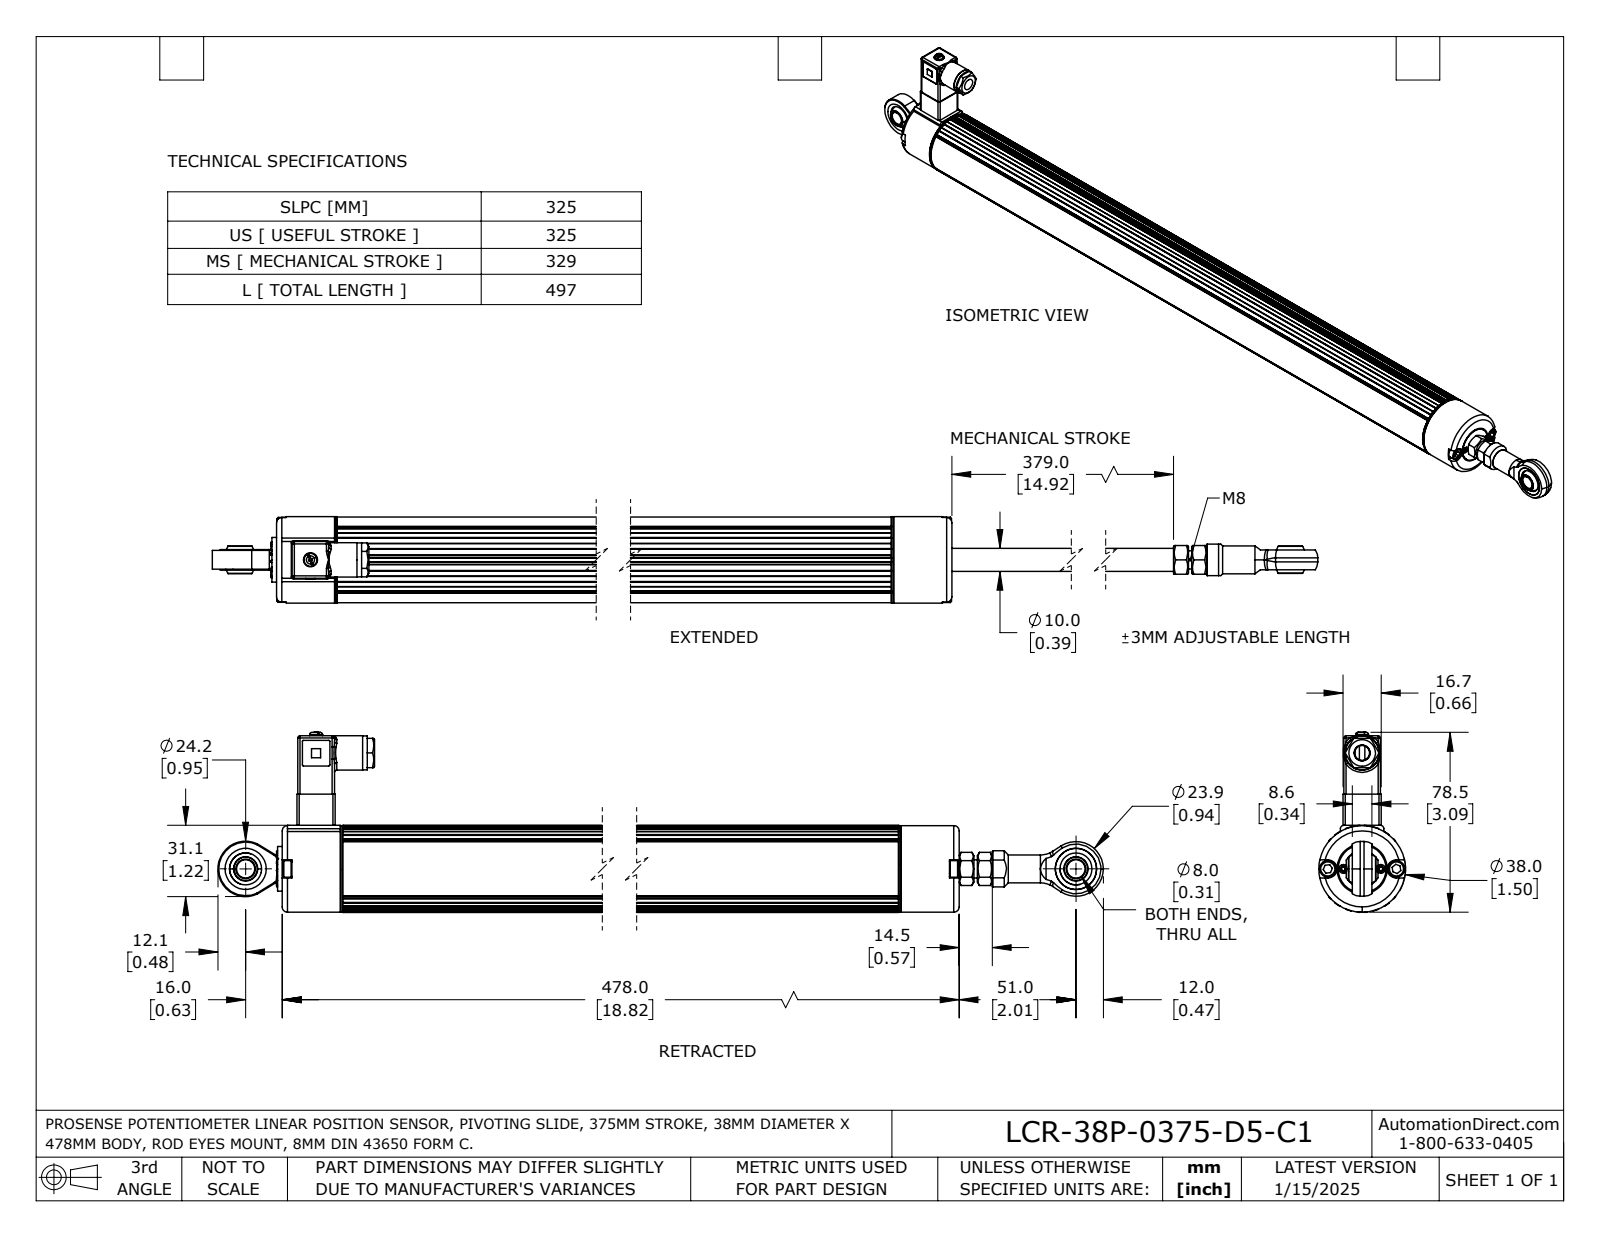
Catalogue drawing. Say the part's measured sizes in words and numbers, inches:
The part is named "LCR-38P-0375-D5-C1". Its 3-D file was written by "SolidWorks 2023 (AUTOMOTIVE_DESIGN)". It is 11 solids with 657 faces: 295 planar, 210 cylindrical and 152 other. Overall it measures 22.404 by 3.093 by 1.488 inches. Its volume is 33.28 cubic inches and its surface area 148.3 square inches. Round holes: 6 of diameter 0.102, 4 of diameter 0.091, 3 of diameter 0.315, 3 of diameter 0.551, 2 of diameter 0.094, 2 of diameter 0.1, 2 of diameter 0.111, 2 of diameter 0.134, 2 of diameter 0.152, 2 of diameter 0.165, 1 of diameter 0.079, 1 of diameter 0.118. Round bosses or shafts: 6 of diameter 0.063, 4 of diameter 0.283, 4 of diameter 0.15, 2 of diameter 0.48, 2 of diameter 0.079, 1 of diameter 1.488, 1 of diameter 0.823, 1 of diameter 0.768. Partial cylindrical surfaces (rounded edges, fillets, slot ends): 32 of radius 0.008, 20 of radius 0.039, 12 of radius 0.02, 6 of radius 0.016, 2 of radius 0.012, 2 of radius 0.059, 2 of radius 0.083, 2 of radius 0.098. The main face-to-face distances are 16.732, 1.043, 17.776, 0.031, 0.045, 0.612, 0.598, 0.014, 0.644, 0.138. The hole center spacings are 0.632, 0.075, 0.634, 0.264, 0.268, 0.285, 0.323, 0.394.
